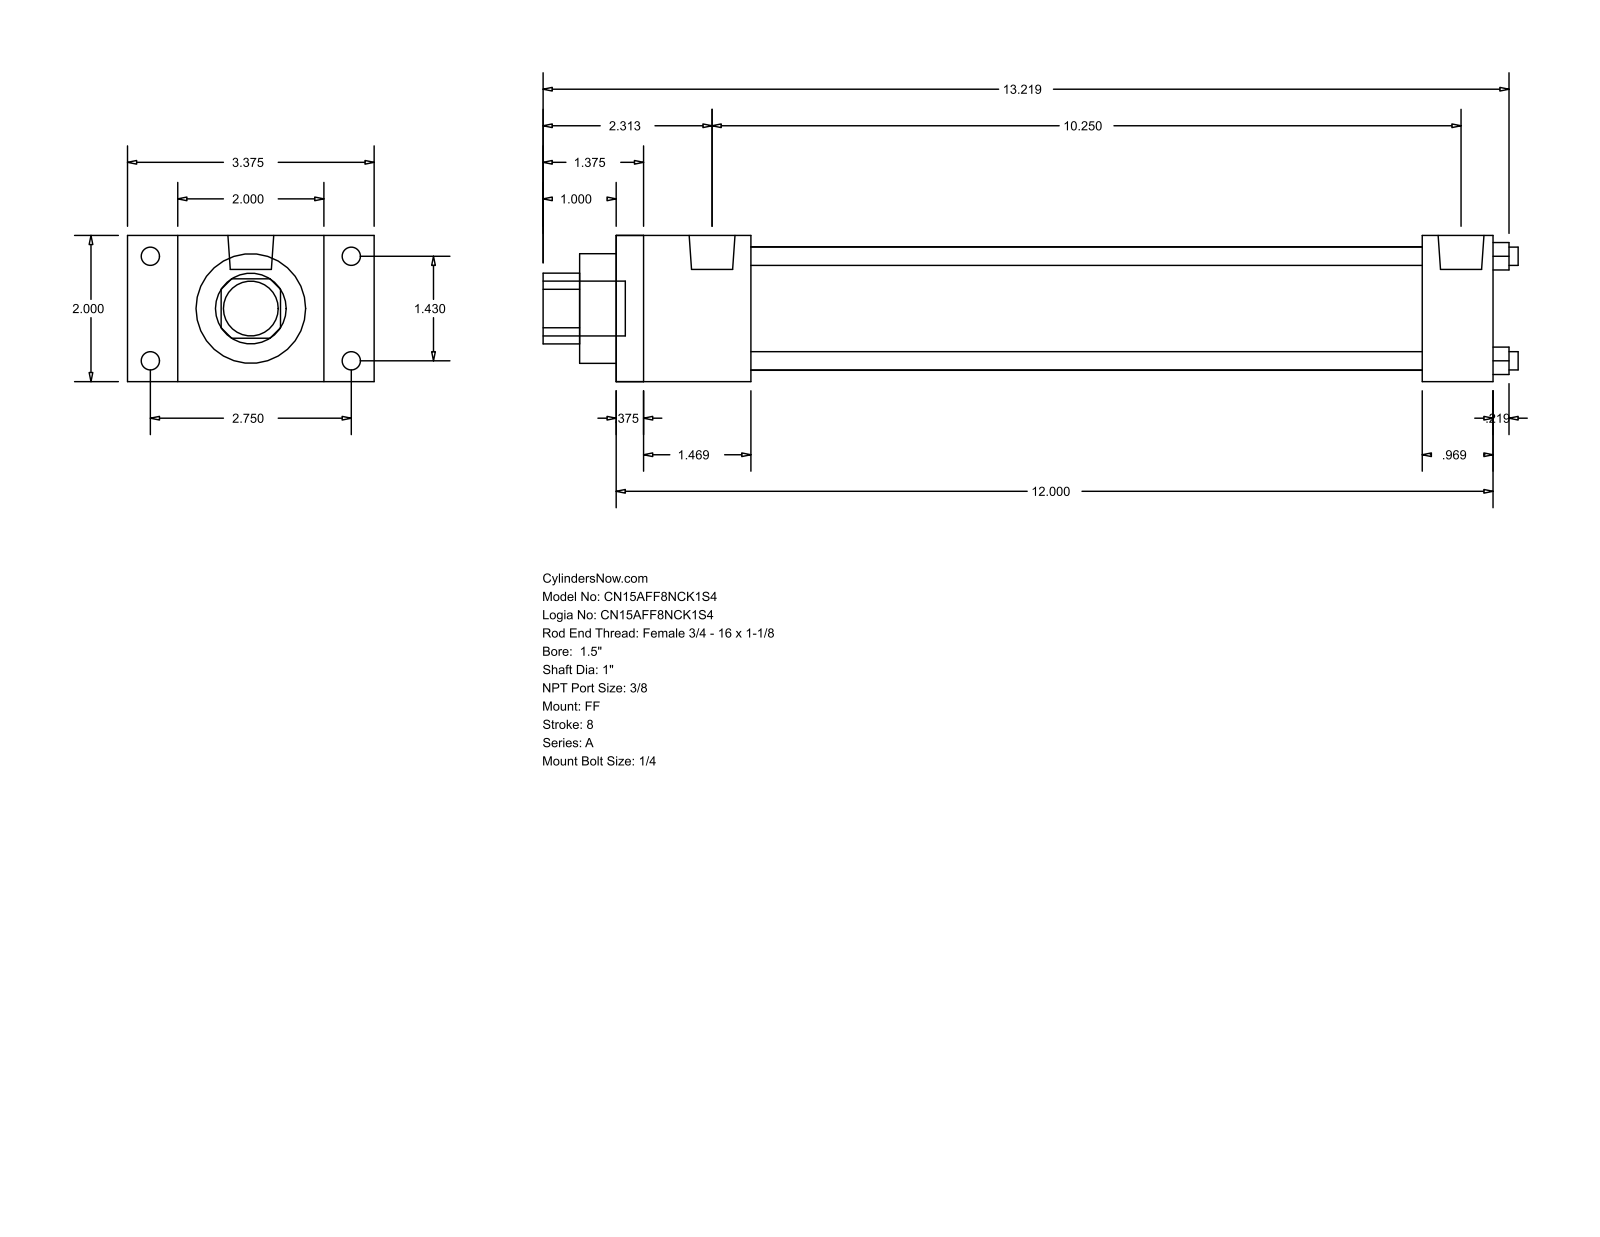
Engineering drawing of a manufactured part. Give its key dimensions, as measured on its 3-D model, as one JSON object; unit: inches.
{"part_name": "A_FF__0150_1", "step_written_by": "GSSL Pune (CONFIG_CONTROL_DESIGN)", "units": "inches", "bodies": {"solids": 0, "faces": 92, "planar": 64, "cylindrical": 28, "other": 0}, "overall_size": [13.344, 3.375, 2], "round_holes": [[0.25, 4], [1, 1], [1.5, 1], [1.69, 1]], "round_bosses_or_shafts": [[0.25, 4], [0.219, 4], [0.627, 2], [0.75, 1]], "partial_cylinders_radius": [[0.484, 1]], "face_to_face_distances": [2, 12, 0.375, 11.625, 1.844, 11.031, 1.469, 10.656, 9.187, 10.156], "hole_center_spacings": [1.011, 1.43, 2.022]}
